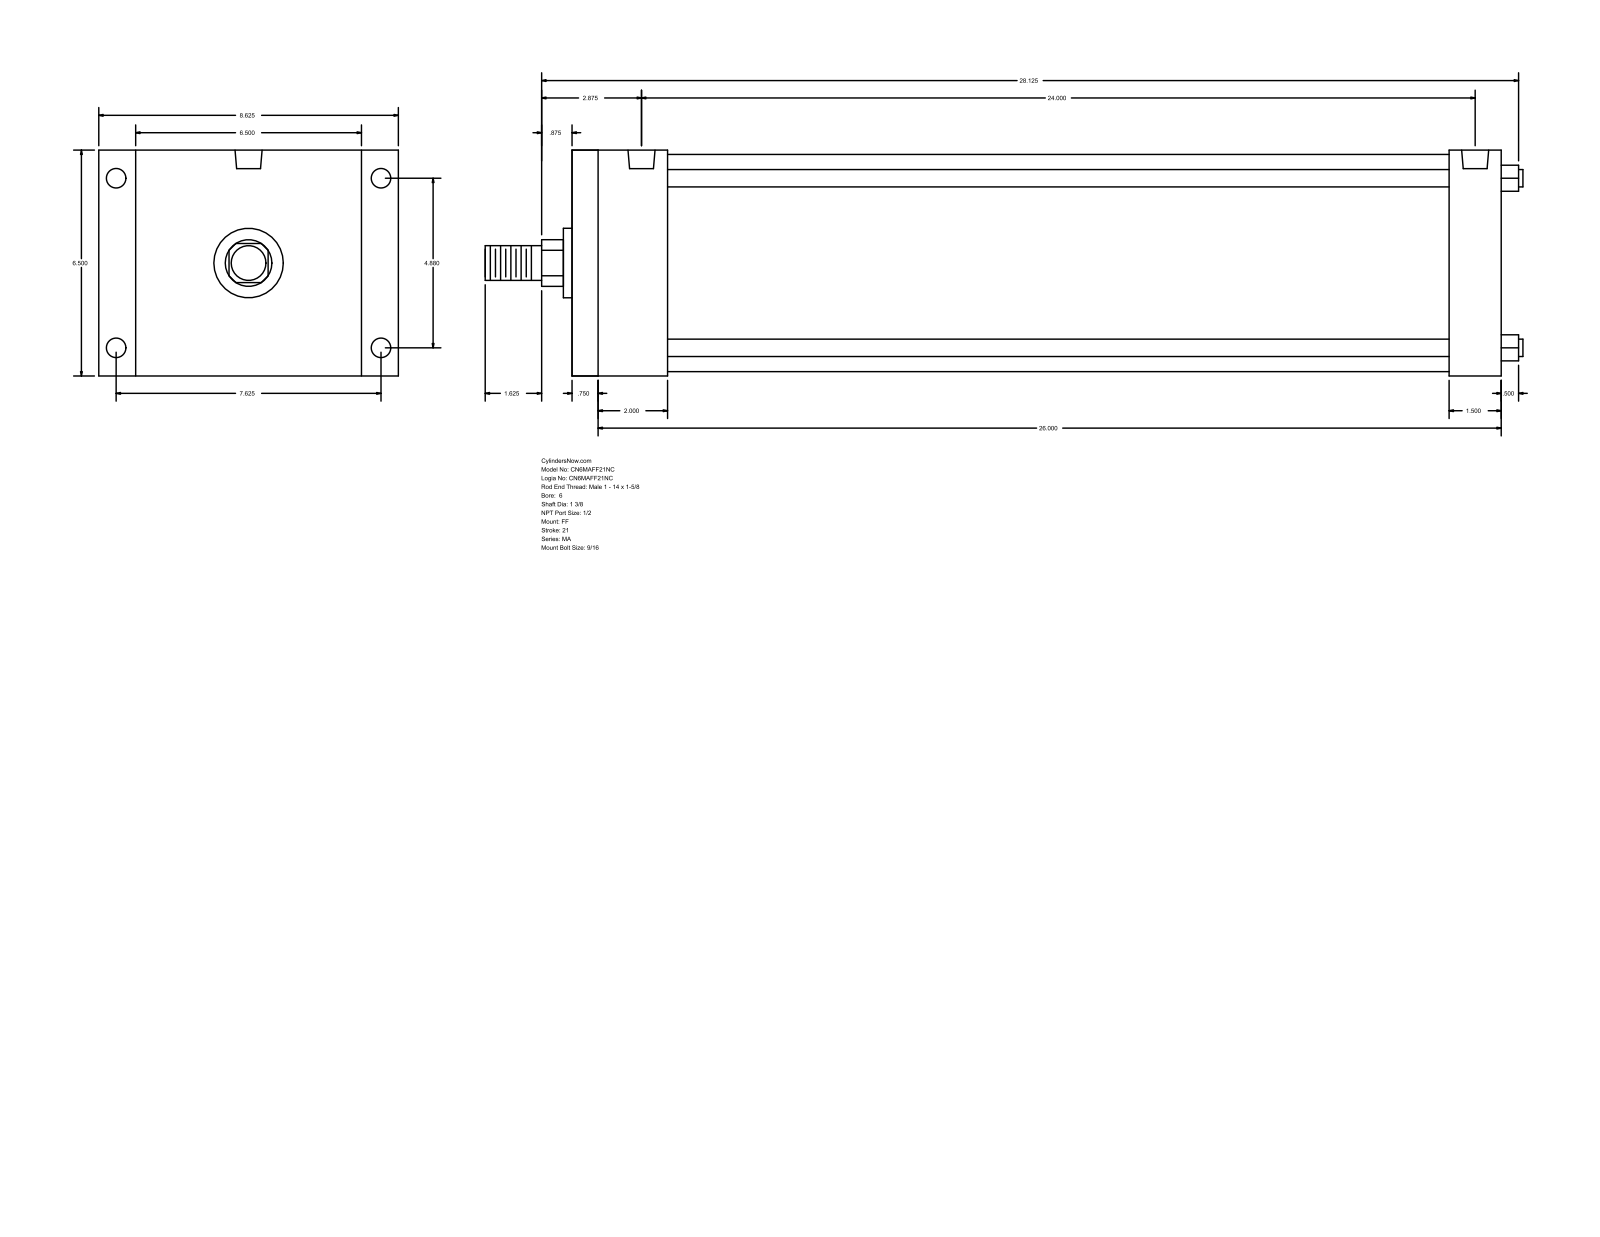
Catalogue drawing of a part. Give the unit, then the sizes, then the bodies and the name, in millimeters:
Units: millimetres
Overall size (bounding box): 758.83 × 219.07 × 165.1
Round holes (diameter × count): ⌀14.29 ×4, ⌀17.46 ×4, ⌀19.77 ×2
Round bosses / shafts (diameter × count): ⌀12.7 ×4, ⌀158.75 ×1, ⌀50.8 ×1, ⌀34.92 ×1, ⌀25.4 ×1
Partial cylindrical surfaces — rounded edges, fillets, slot ends (radius × count): R17.06 ×1
Main face-to-face distances: 165.1, 679.44, 15.87, 663.57, 50.8, 625.48, 66.67, 612.77, 641.35, 574.68
Hole centre spacings: 123.96, 193.68, 229.95, 612.77, 3.18, 609.59
Bodies: 0 solids, 92 faces (64 planar, 28 cylindrical, 0 other)
Part name (STEP PRODUCT): MA_FF__0600_1.375
STEP written by: GSSL Pune (CONFIG_CONTROL_DESIGN)
